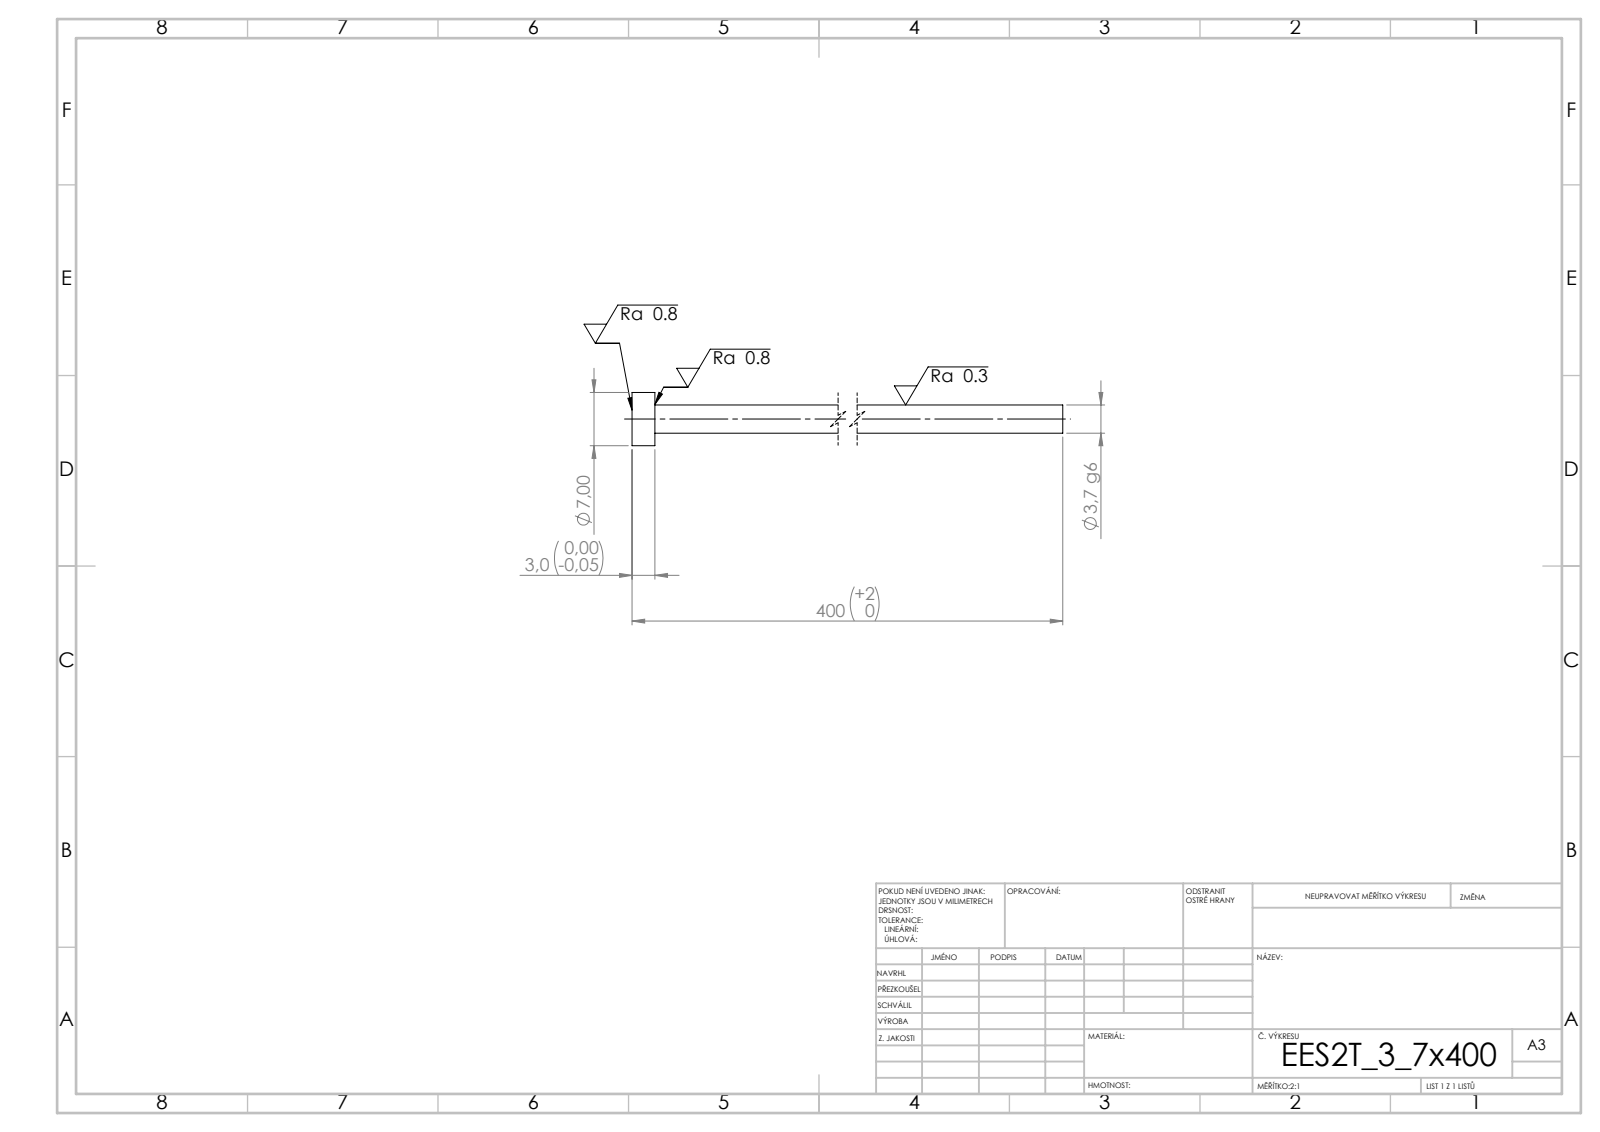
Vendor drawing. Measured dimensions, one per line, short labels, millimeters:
written by: SolidWorks 2019 (CONFIG_CONTROL_DESIGN)
unit: mm
bodies: 1 solid, 7 faces (3 planar, 4 cylindrical, 0 other)
size: 400 × 7 × 7
volume: 4 384 mm³; area: 4 758 mm²
bosses: 1× ⌀7, 1× ⌀3.7
face distances: 3, 400, 397
